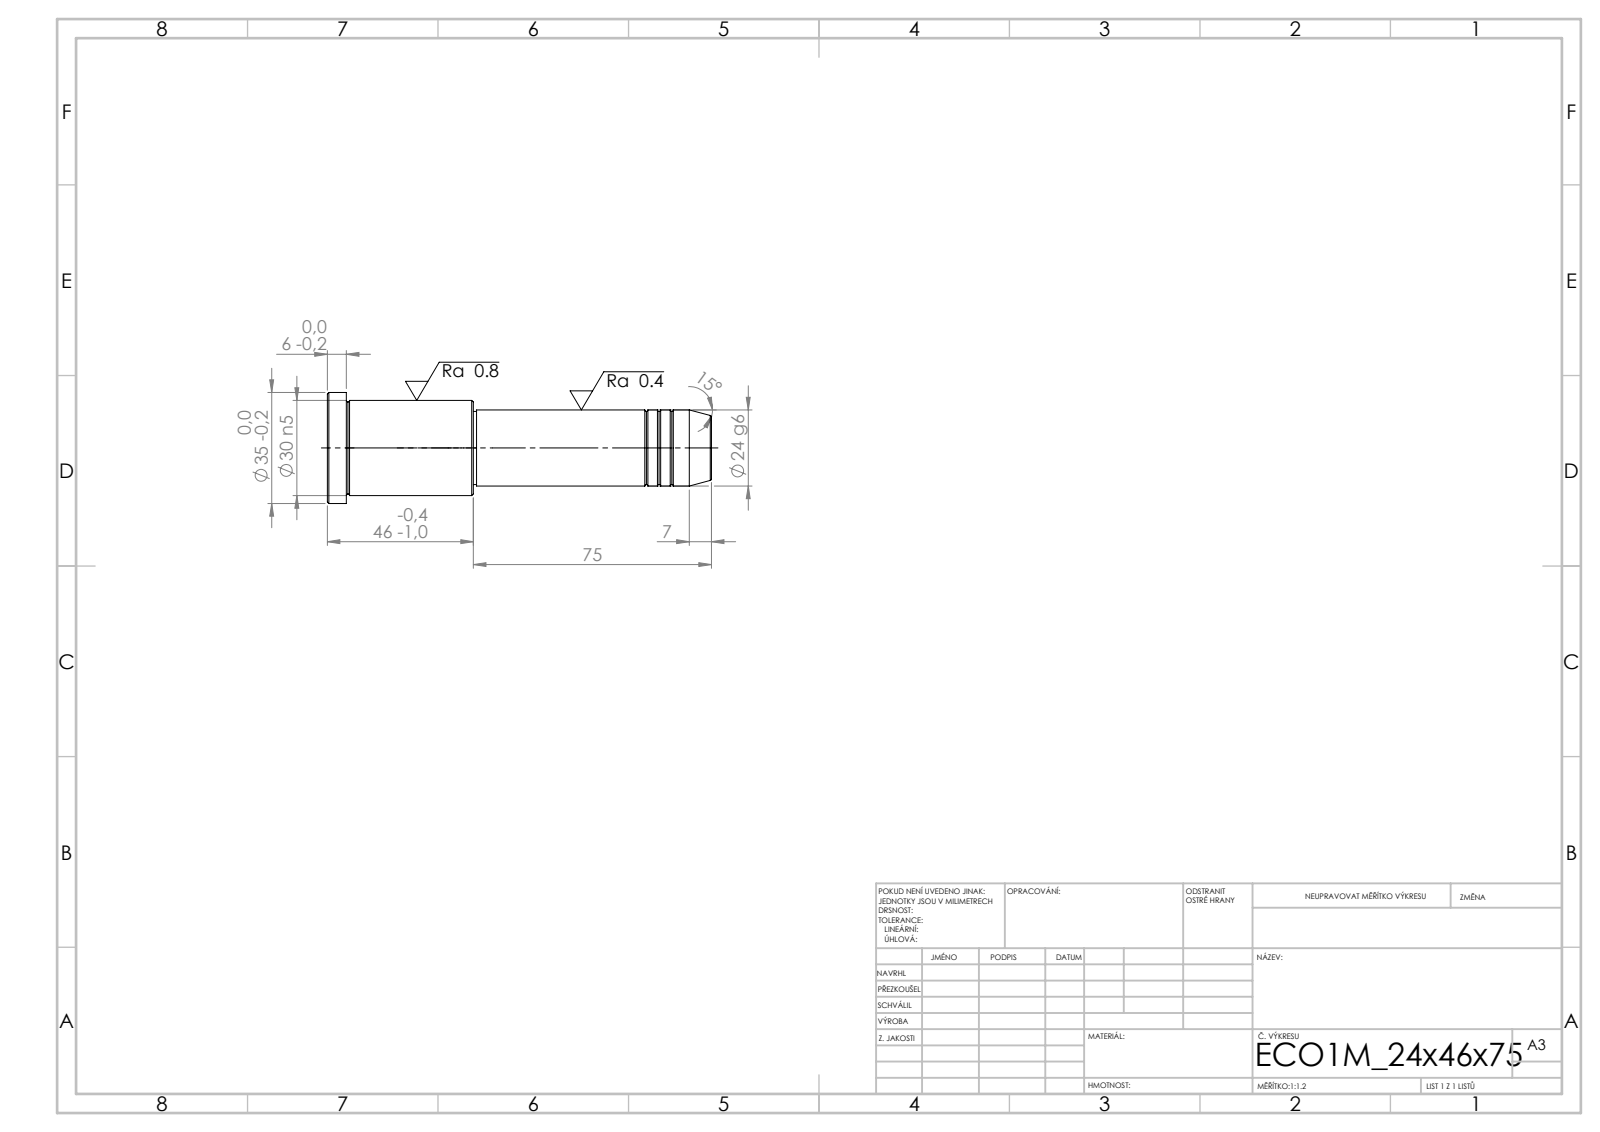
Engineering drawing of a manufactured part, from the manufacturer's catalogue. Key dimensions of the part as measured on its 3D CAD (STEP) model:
STEP written by: SolidWorks 2019 (CONFIG_CONTROL_DESIGN)
Units: millimetres
Bodies: 1 solid, 43 faces (5 planar, 14 cylindrical, 24 other)
Overall size (bounding box): 121 × 35 × 35
Volume: 67 319 mm³ · Surface area: 12 028 mm²
Round bosses / shafts (diameter × count): ⌀35 ×1, ⌀30 ×1, ⌀24 ×1, ⌀23 ×1
Main face-to-face distances: 121, 115, 6, 75, 40, 46, 74, 1, 41, 47
